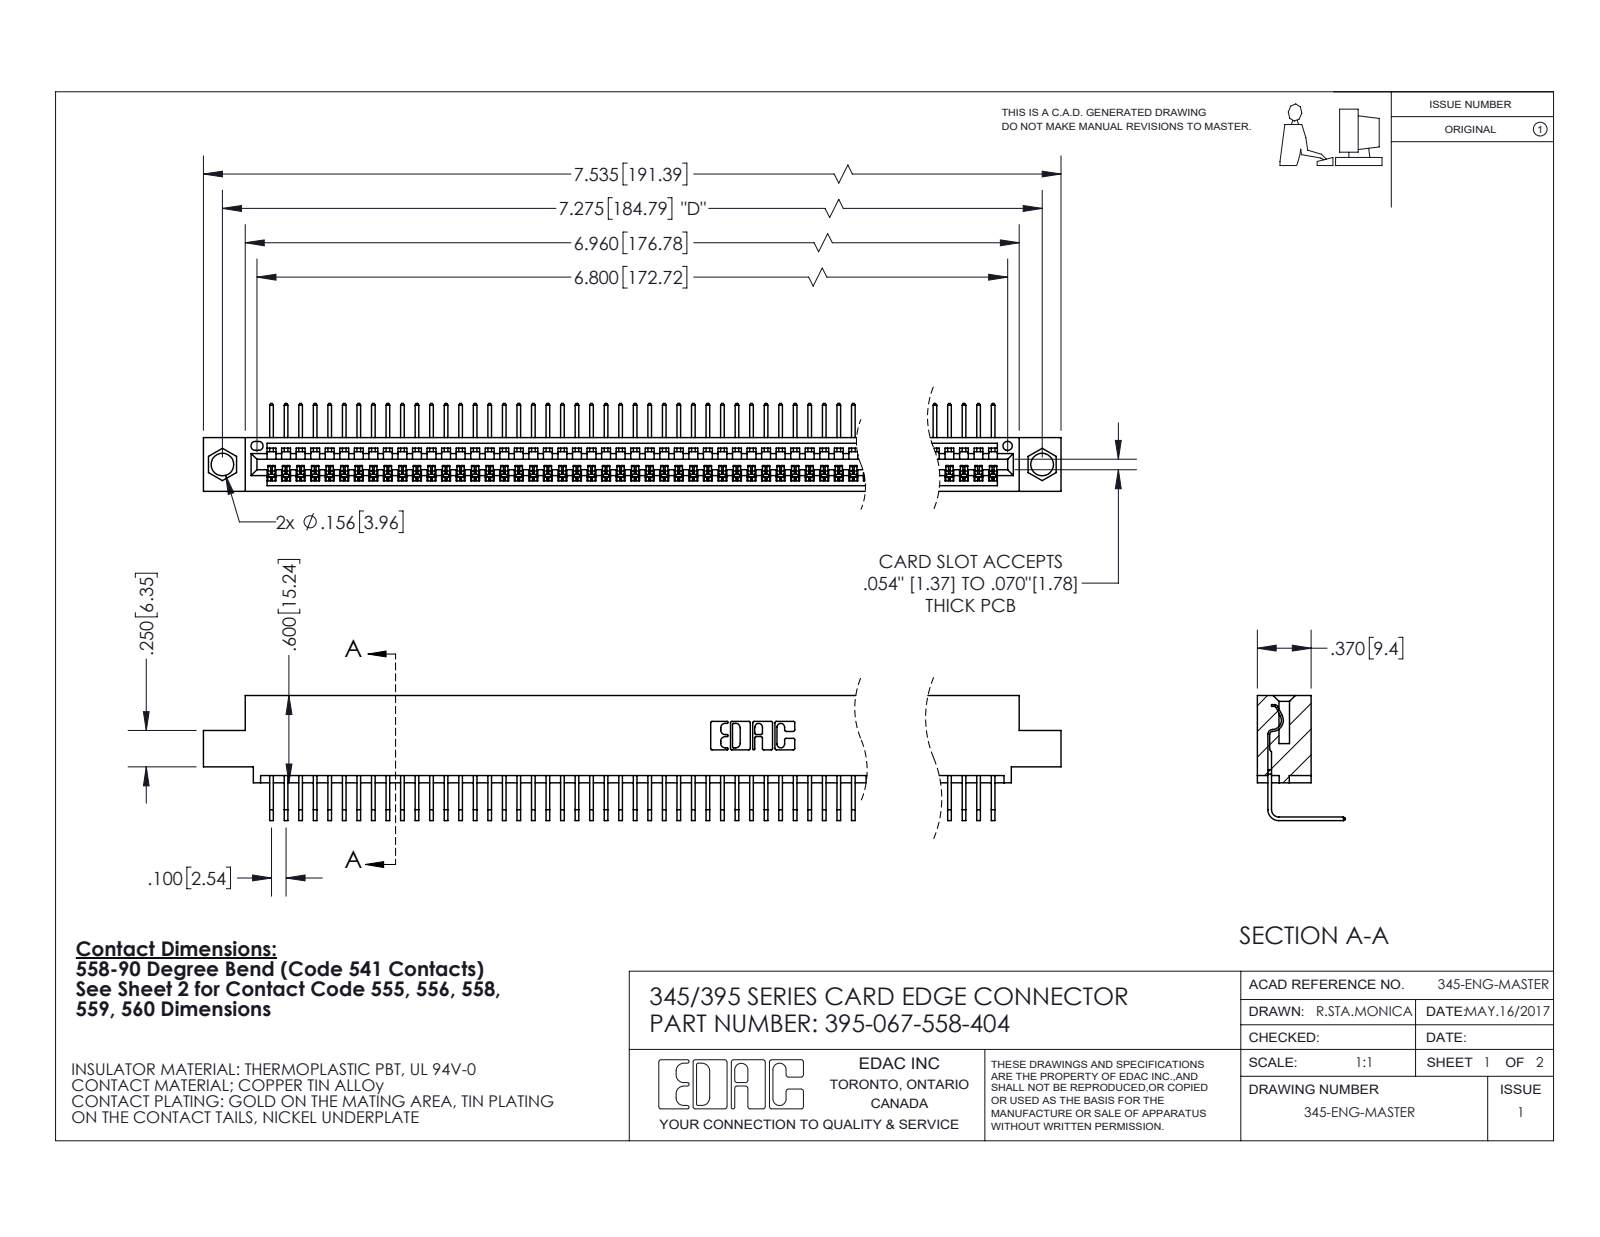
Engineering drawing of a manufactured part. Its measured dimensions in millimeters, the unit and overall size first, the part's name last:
Units: millimetres
Overall size (bounding box): 191.4 × 21.8 × 15.4
Round holes (diameter × count): ⌀4 ×2, ⌀1.6 ×1
Partial cylindrical surfaces — rounded edges, fillets, slot ends (radius × count): R0.2 ×134, R0.3 ×22, R0.2 ×6, R0.8 ×6, R0.7 ×3, R0.8 ×2, R1 ×2, R0.4 ×1
Main face-to-face distances: 1.8, 7.6, 9.4, 5.1, 2.5, 6.9, 0.6, 5.7, 3.8, 1.8
Hole centre spacings: 6.9, 178.8, 184.8
Volume: 18 420 mm³ · Surface area: 26 060 mm²
Bodies: 68 solids, 4164 faces (2912 planar, 1252 cylindrical, 0 other)
Part name (STEP PRODUCT): 345 Part_0.110 Offset - 0.156 Dia-TI; 345-292-001_558 Tail - 2; 395-067-558-404
STEP written by: SolidWorks 2020 (CONFIG_CONTROL_DESIGN)
